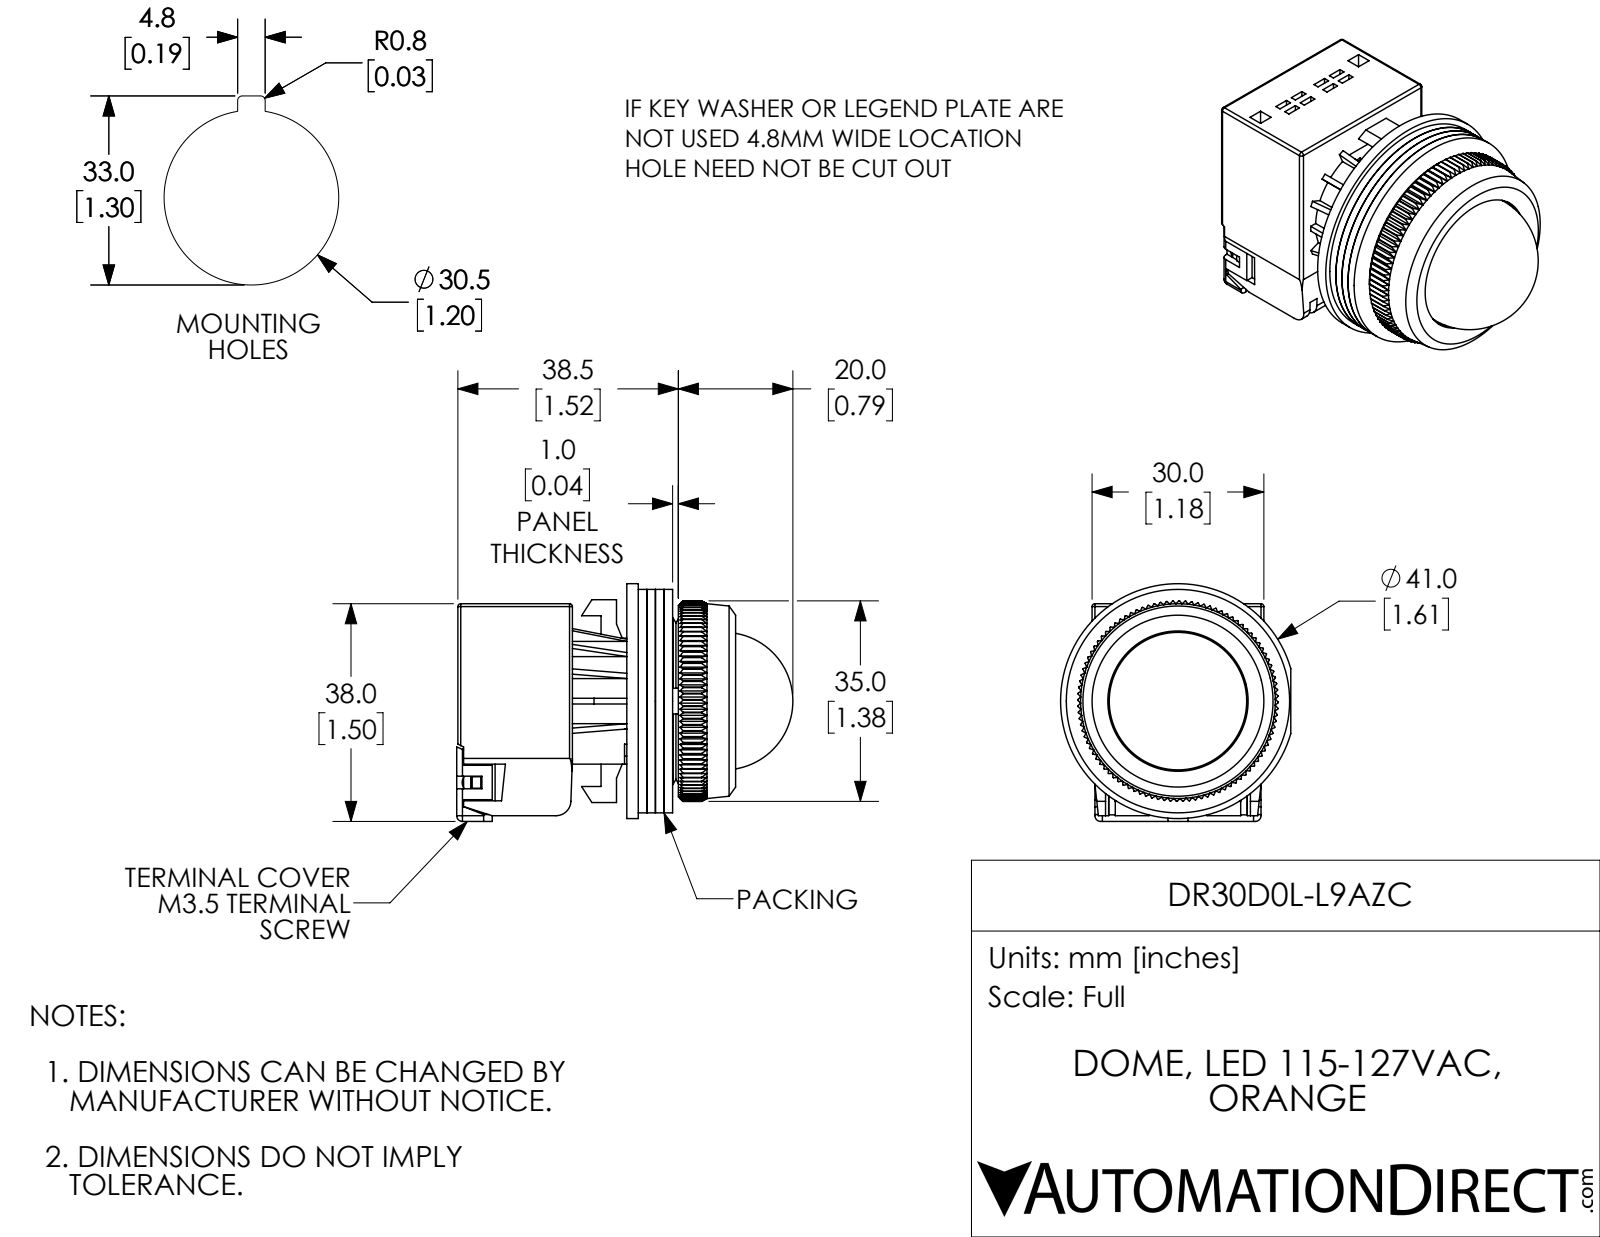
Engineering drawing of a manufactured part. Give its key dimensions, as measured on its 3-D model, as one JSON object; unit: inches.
{"part_name": "DR30D0L-L9AZC", "step_written_by": "SolidWorks 2017 (AUTOMOTIVE_DESIGN)", "units": "inches", "bodies": {"solids": 18, "faces": 1544, "planar": 945, "cylindrical": 353, "other": 246}, "overall_size": [2.309, 1.634, 1.583], "volume_in3": 2.184, "surface_area_in2": 48.71, "round_holes": [[0.118, 2], [0.122, 2], [0.138, 2], [0.276, 2], [0.362, 1], [0.433, 1], [0.461, 1], [0.543, 1], [0.563, 1], [0.583, 1], [0.63, 1], [0.72, 1]], "round_bosses_or_shafts": [[0.232, 2], [1.614, 1], [1.535, 1], [1.16, 1], [0.945, 1], [0.858, 1], [0.819, 1], [0.799, 1]], "partial_cylinders_radius": [[0.039, 14], [0.008, 8], [0.02, 8], [0.065, 3], [0.029, 1], [0.068, 1], [0.079, 1], [0.102, 1]], "face_to_face_distances": [0.059, 0.118, 0.177, 0.039, 0.315, 0.197, 0.512, 0.689, 0.374, 1.161], "hole_center_spacings": [0.704, 0.63]}
